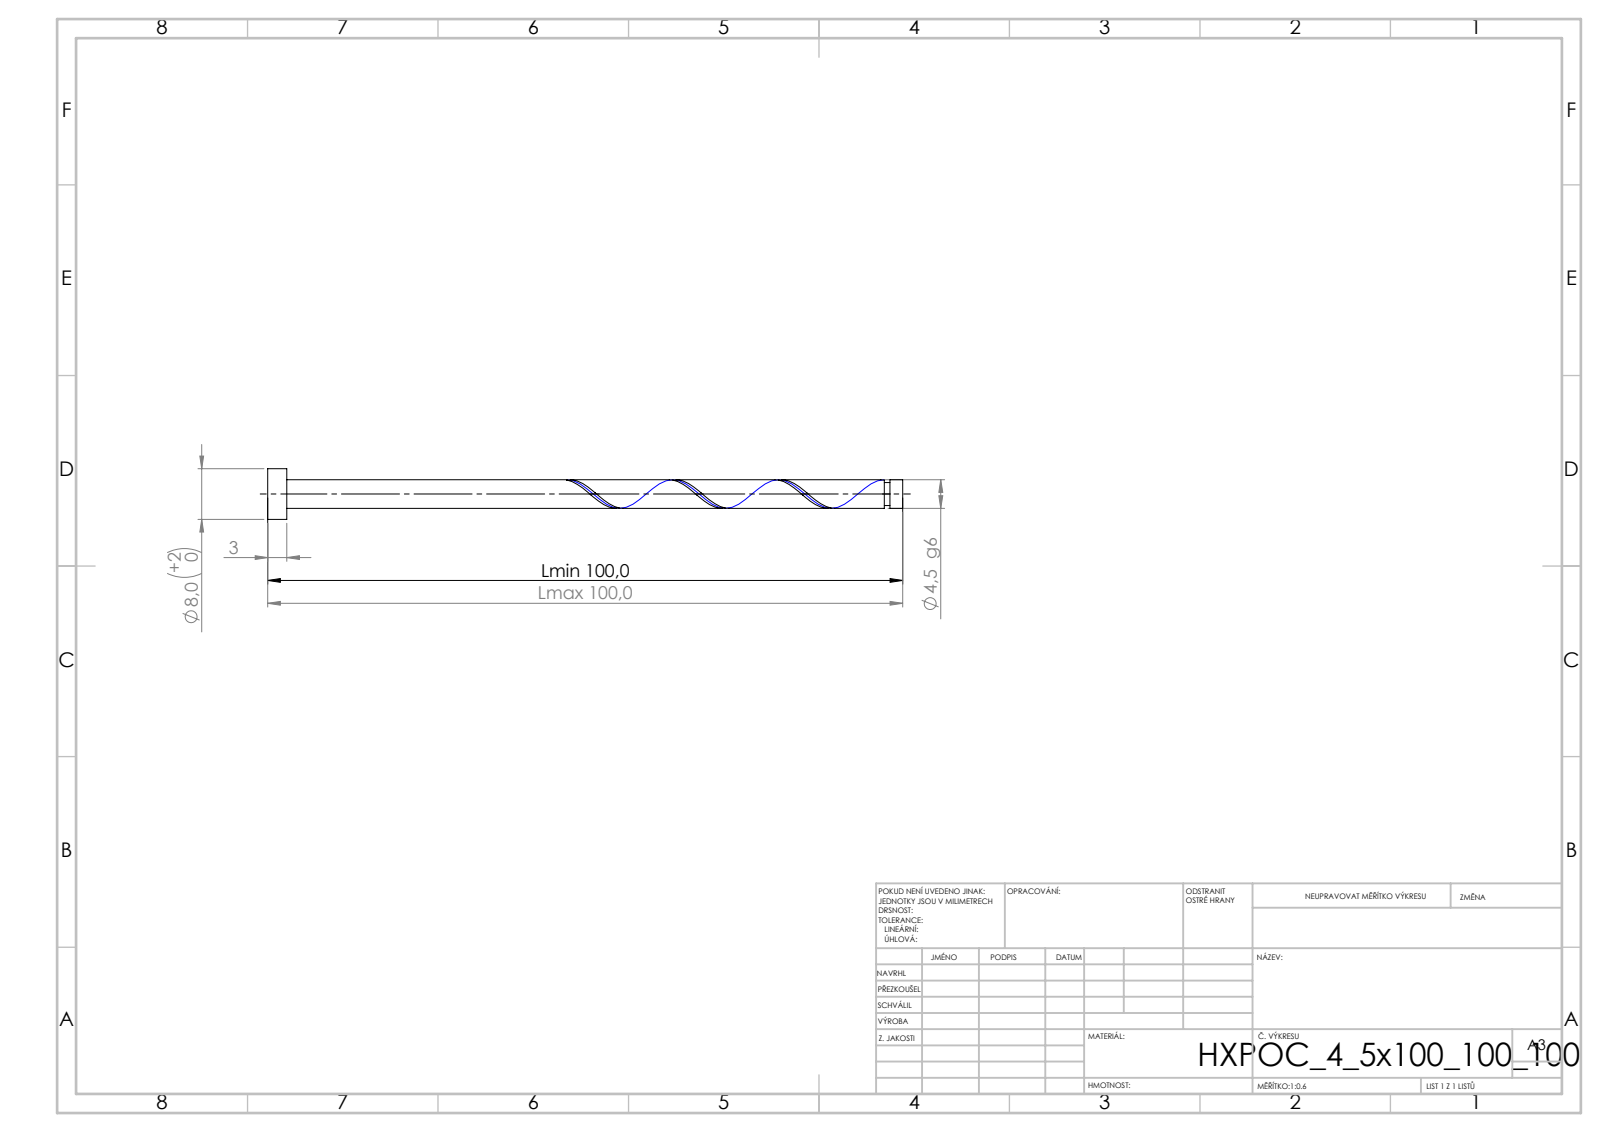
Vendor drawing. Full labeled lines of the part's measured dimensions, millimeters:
STEP written by: SolidWorks 2019 (CONFIG_CONTROL_DESIGN)
Units: millimetres
Bodies: 1 solid, 21 faces (6 planar, 14 cylindrical, 1 other)
Overall size (bounding box): 100 × 8 × 8
Volume: 1 673 mm³ · Surface area: 1 587 mm²
Round bosses / shafts (diameter × count): ⌀8 ×1, ⌀4.5 ×1, ⌀3.6 ×1
Main face-to-face distances: 3, 100, 97, 98, 95, 2, 97.1, 94.1, 0.9, 2.9
